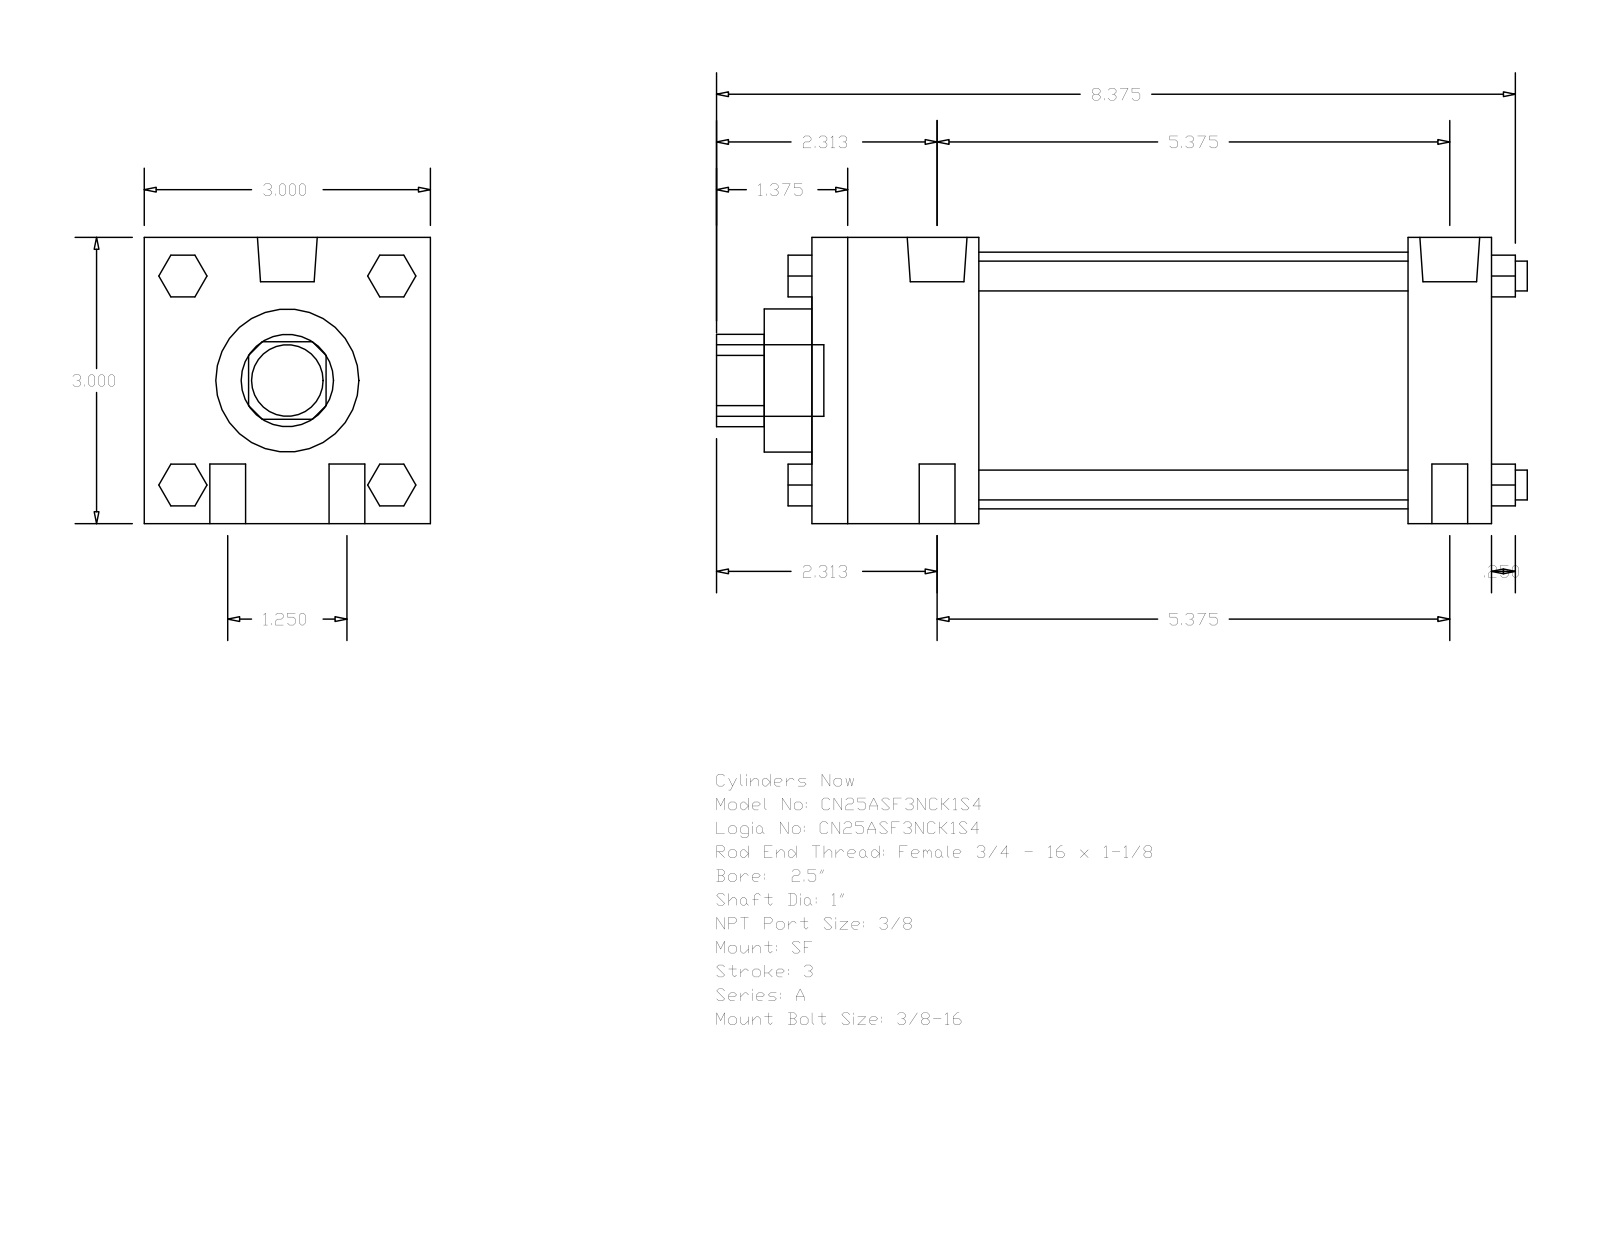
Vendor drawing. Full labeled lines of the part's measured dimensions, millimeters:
Part name (STEP PRODUCT): A_SF__0250_1
STEP written by: GSSL Pune (CONFIG_CONTROL_DESIGN)
Units: millimetres
Bodies: 0 solids, 124 faces (94 planar, 30 cylindrical, 0 other)
Overall size (bounding box): 215.9 × 76.2 × 76.2
Round holes (diameter × count): ⌀25.4 ×1, ⌀38.1 ×1, ⌀68.33 ×1
Round bosses / shafts (diameter × count): ⌀9.53 ×4, ⌀7.94 ×4, ⌀15.93 ×2, ⌀5.56 ×2, ⌀19.05 ×1
Partial cylindrical surfaces — rounded edges, fillets, slot ends (radius × count): R12.29 ×1
Main face-to-face distances: 76.2, 180.98, 158.75, 22.23, 44.45, 114.3, 136.53, 12.7, 11.11, 57.15
